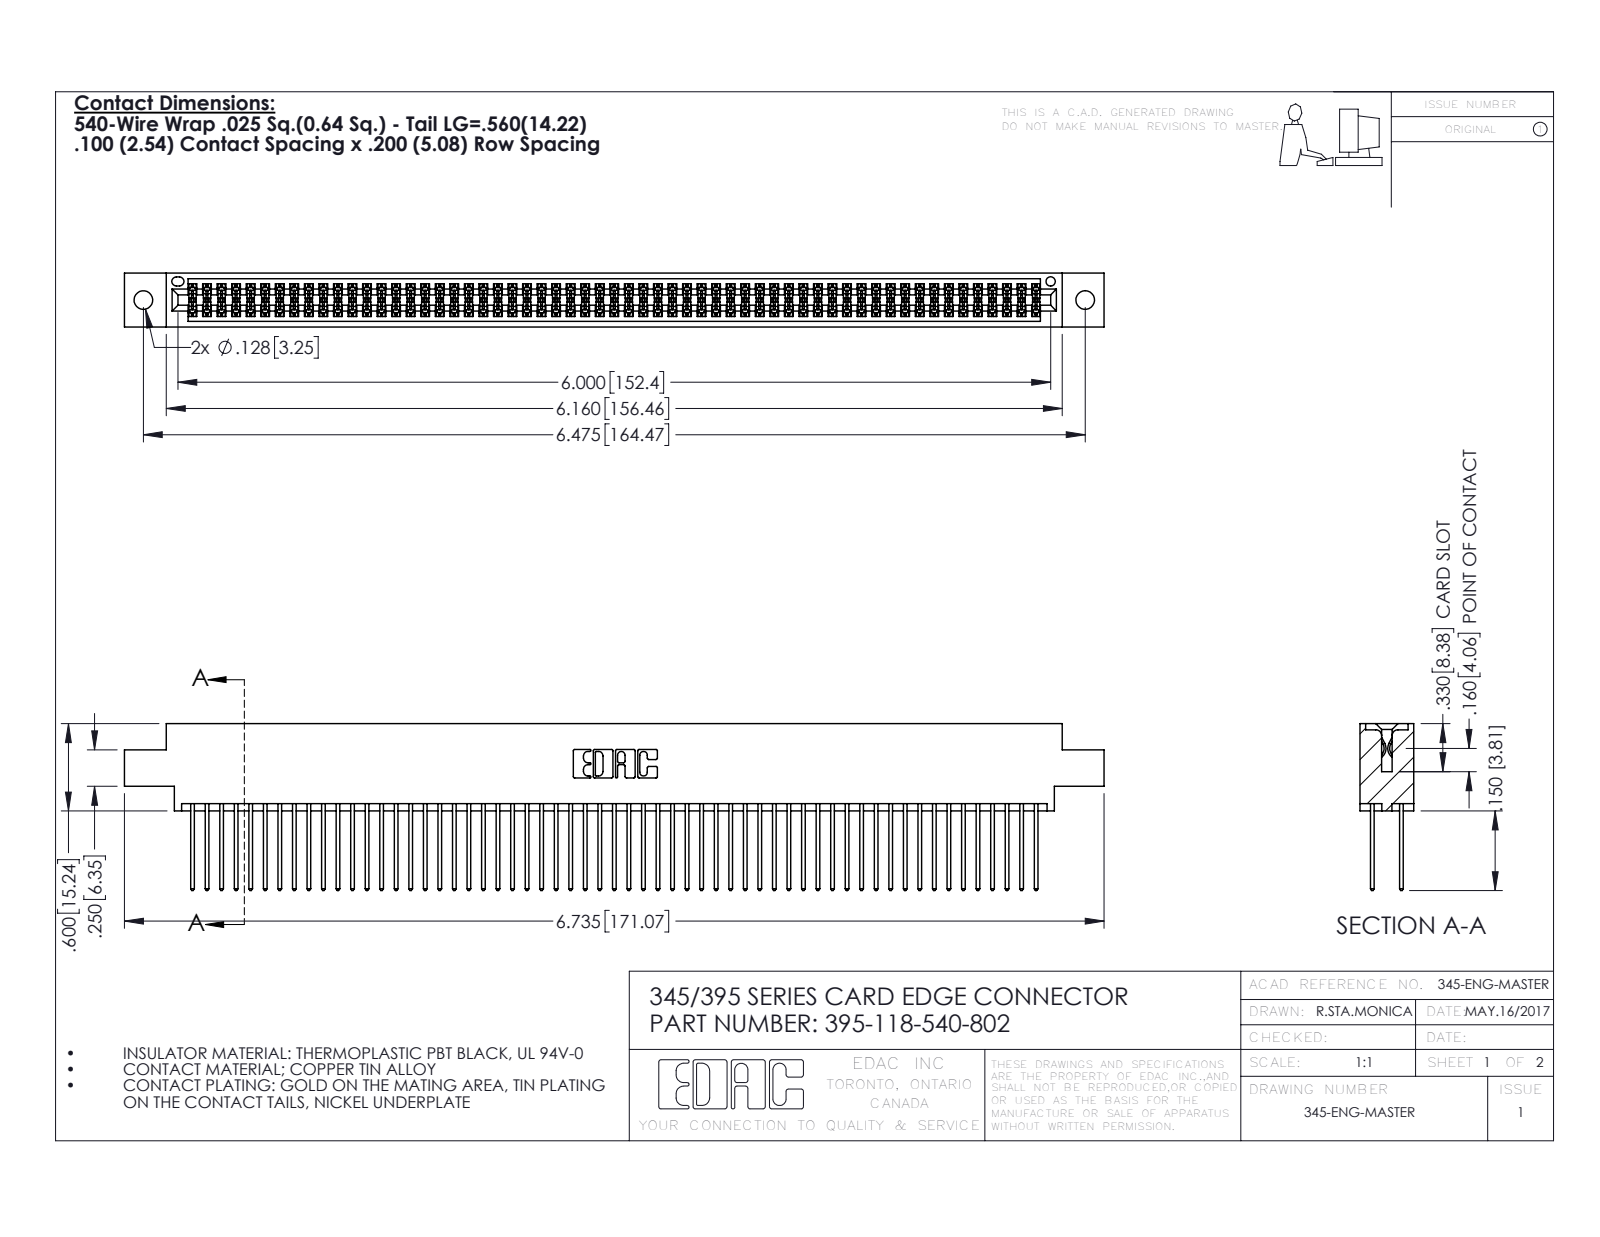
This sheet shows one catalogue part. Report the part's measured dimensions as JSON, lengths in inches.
{"part_name": "395-118-540-802; 345 Part_0.170 Offset - 0.128 Dia; 345-292-001_345-293-140", "step_written_by": "SolidWorks 2016 (CONFIG_CONTROL_DESIGN)", "units": "inches", "bodies": {"solids": 119, "faces": 6030, "planar": 3978, "cylindrical": 2052, "other": 0}, "overall_size": [6.735, 1.147, 0.37], "volume_in3": 1.042, "surface_area_in2": 42.64, "round_holes": [[0.128, 2], [0.064, 1]], "partial_cylinders_radius": [[0.006, 177], [0.01, 118], [0.01, 22], [0.007, 6], [0.031, 6], [0.026, 3], [0.014, 2], [0.019, 2]], "face_to_face_distances": [0.298, 0.072, 0.2, 0.098, 0.272, 0.025, 0.37, 0.225, 0.175, 0.149], "hole_center_spacings": [0.27, 6.239, 6.475]}
